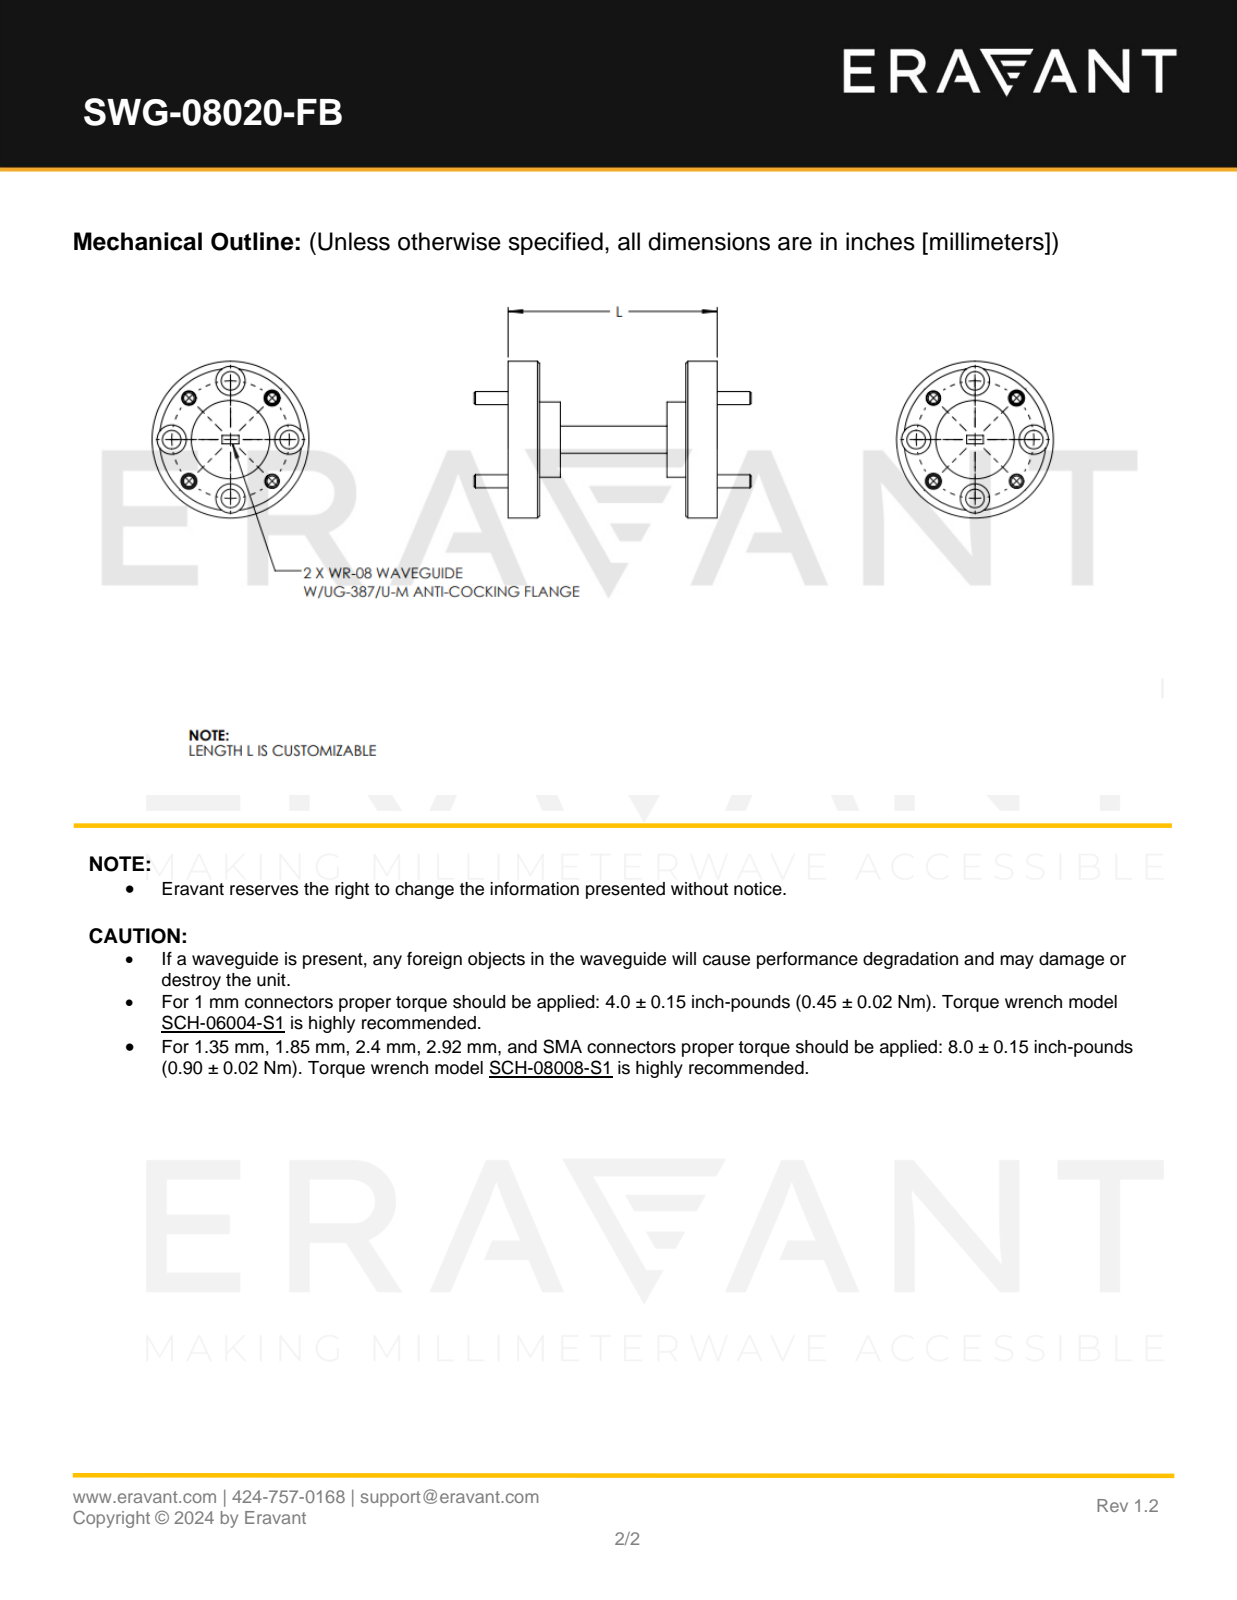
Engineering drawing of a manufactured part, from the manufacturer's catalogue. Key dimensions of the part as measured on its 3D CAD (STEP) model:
Part name (STEP PRODUCT): SWG-08020-F1
STEP written by: SolidWorks 2013 (CONFIG_CONTROL_DESIGN)
Units: inches
Bodies: 5 solids, 140 faces (32 planar, 68 cylindrical, 40 other)
Overall size (bounding box): 2.305 × 0.75 × 0.75
Volume: 0.161 in³ · Surface area: 4.588 in²
Round holes (diameter × count): ⌀0.06 ×4, ⌀0.067 ×4, ⌀0.089 ×4, ⌀0.14 ×4
Round bosses / shafts (diameter × count): ⌀0.063 ×4, ⌀0.75 ×1, ⌀0.375 ×1, ⌀0.36 ×1
Main face-to-face distances: 0.13, 0.045, 0.085, 1.68, 0.05, 1.81, 1.94, 1.81, 0.13, 0.03
Hole centre spacings: 0.215, 0.398, 0.52, 0.563, 0.398, 0.519, 0.562
